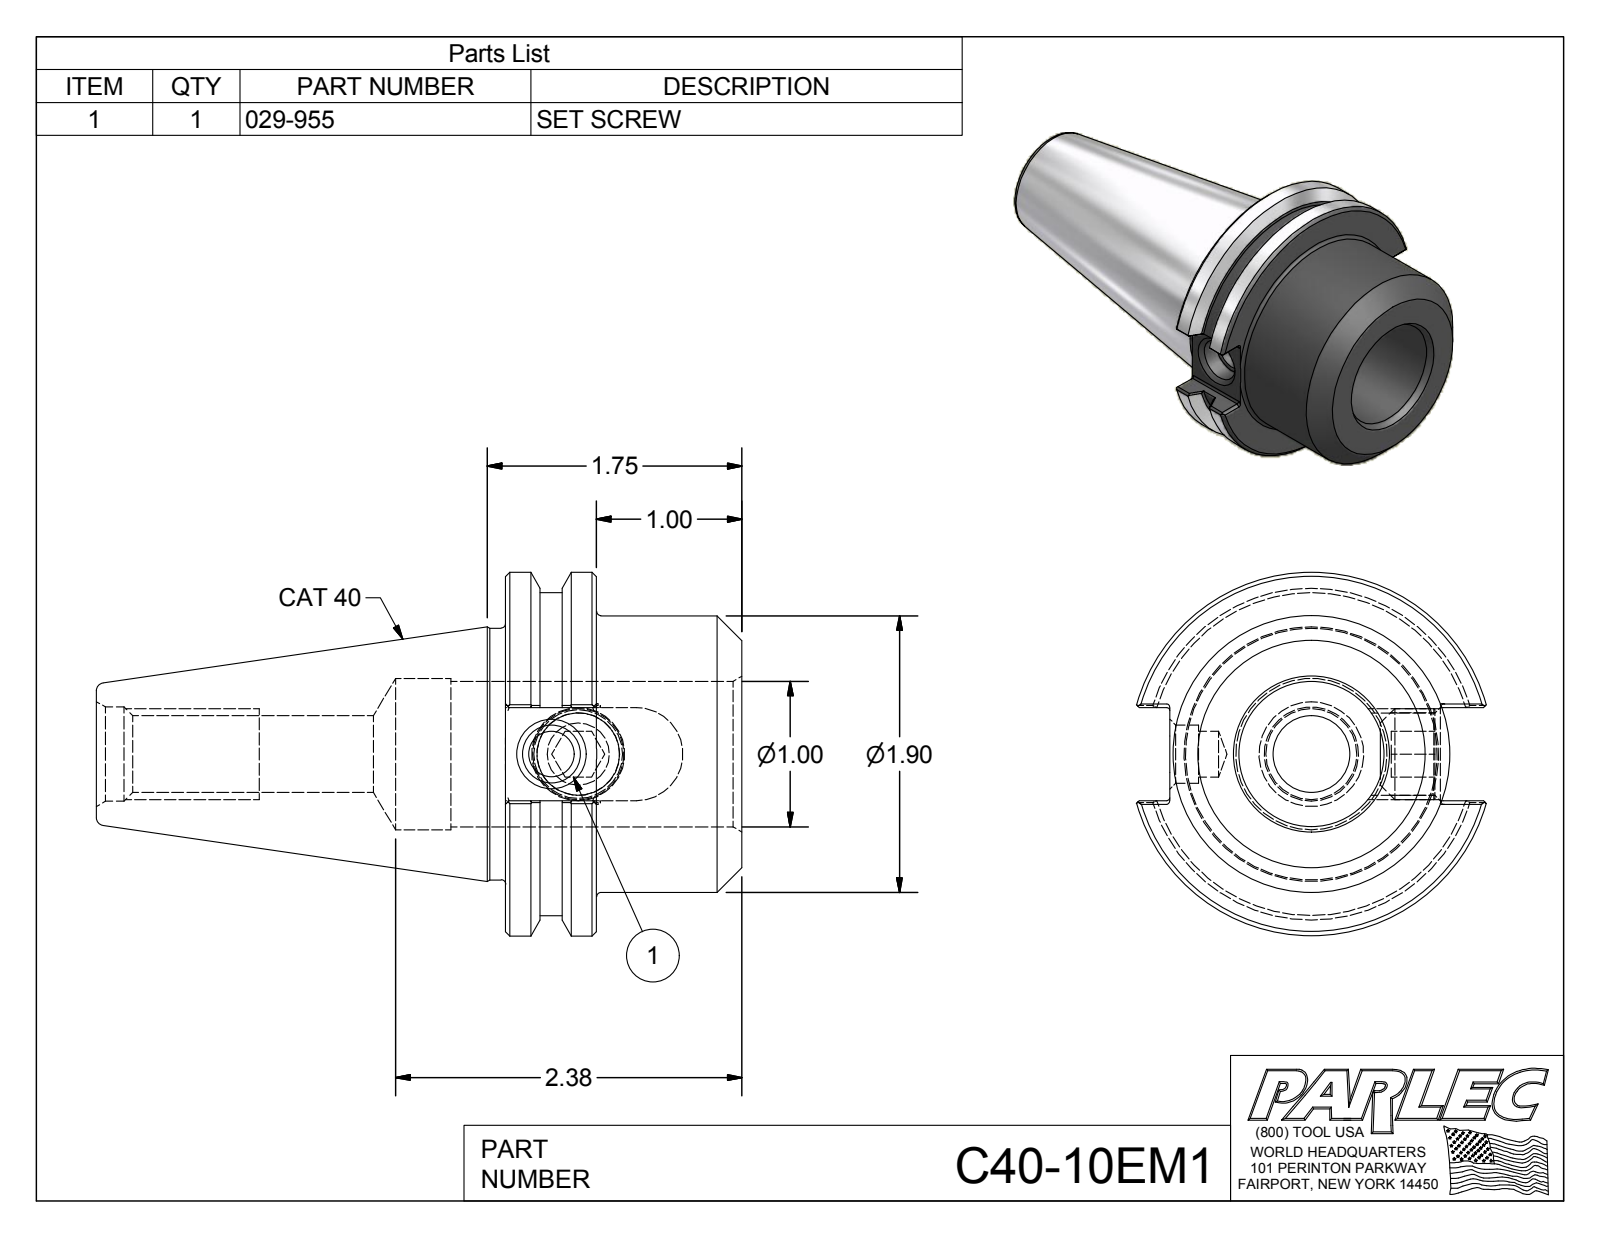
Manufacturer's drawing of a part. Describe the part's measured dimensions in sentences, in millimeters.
The part is named "C40-10EM1; C40-10EM1-1; 029-955". Its 3-D file was written by "Autodesk Inventor 2012 (AUTOMOTIVE_DESIGN)". It is 2 solids with 56 faces: 19 planar, 16 cylindrical and 21 other. Overall it measures 112.7 by 63.5 by 61.4 millimeters. Its volume is 118 200 cubic millimeters and its surface area 27 990 square millimeters. Round holes: 1 of diameter 13.4, 1 of diameter 14.3, 1 of diameter 14.4, 1 of diameter 16.5, 1 of diameter 25.4, 1 of diameter 26.4. Round bosses or shafts: 1 of diameter 63.5, 1 of diameter 56.4, 1 of diameter 48.3, 1 of diameter 44.5, 1 of diameter 15.9. Partial cylindrical surfaces (rounded edges, fillets, slot ends): 1 of radius 8.1. The main face-to-face distances are 15.9, 41.3, 25.4, 16.3, 71.5, 87.3, 112.7, 8, 9.5, 47.5. The hole center spacings are 4.7.
